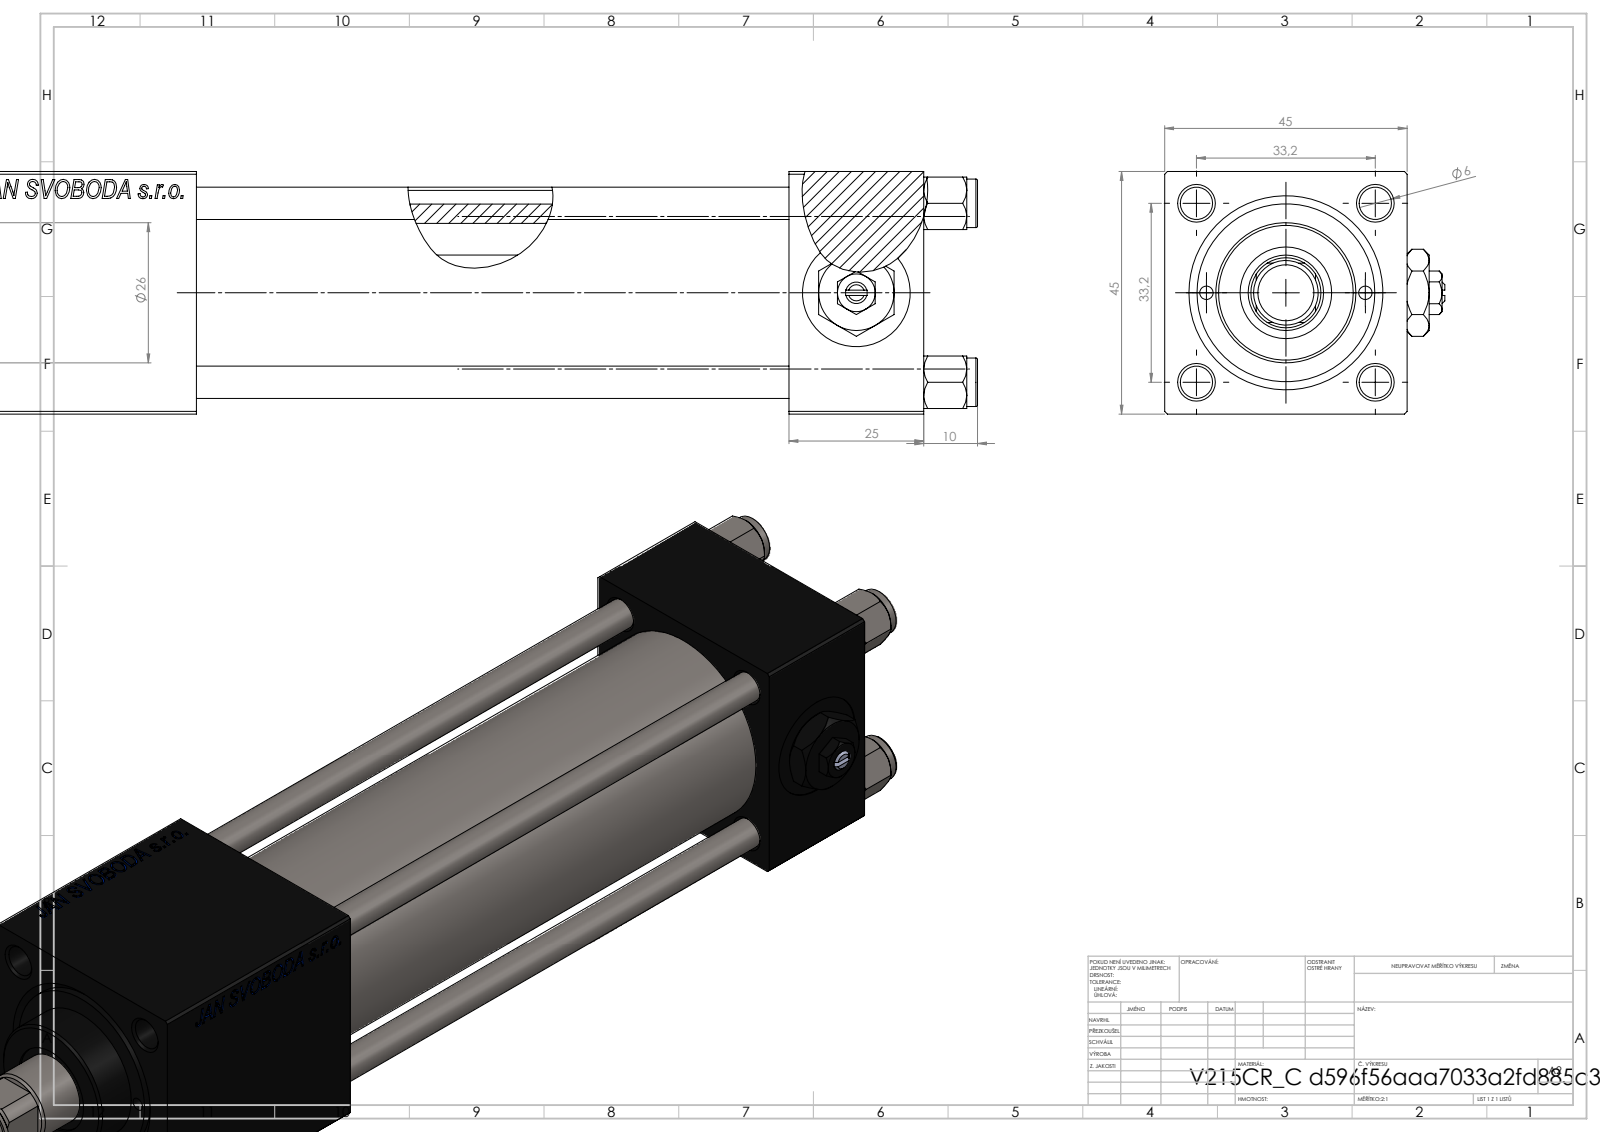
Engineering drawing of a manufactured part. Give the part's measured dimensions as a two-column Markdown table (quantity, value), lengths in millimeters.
| quantity | value |
| --- | --- |
| part name | ROD_END_AH; V215_VC_A; V215CR_C_TYCINKA; V215CR_C_Body (+3 more) |
| STEP written by | SolidWorks 2019 (CONFIG_CONTROL_DESIGN) |
| units | millimeters |
| bodies | 13 solids, 1220 faces (554 planar, 102 cylindrical, 564 other) |
| overall size | 234 × 52 × 45 |
| volume | 230 538 mm³ |
| surface area | 89 449 mm² |
| round holes (diameter × count) | 6 × 4, 2.5 × 2, 7 × 2, 13.16 × 2, 20 × 2, 6.5 × 1, 14 × 1, 17 × 1, 24 × 1, 32 × 1, 33 × 1 |
| round bosses / shafts (diameter × count) | 9 × 4, 38 × 1, 26 × 1, 12 × 1, 10 × 1 |
| partial cylindrical surfaces (radius × count) | 6.5 × 1 |
| main face-to-face distances | 45, 25, 183, 158, 135, 110, 48, 154.3, 129.3, 19.3 |
| hole center spacings | 16.7, 23.48, 33.2, 35.47, 14.75, 46.95, 29.5, 135.5 |
